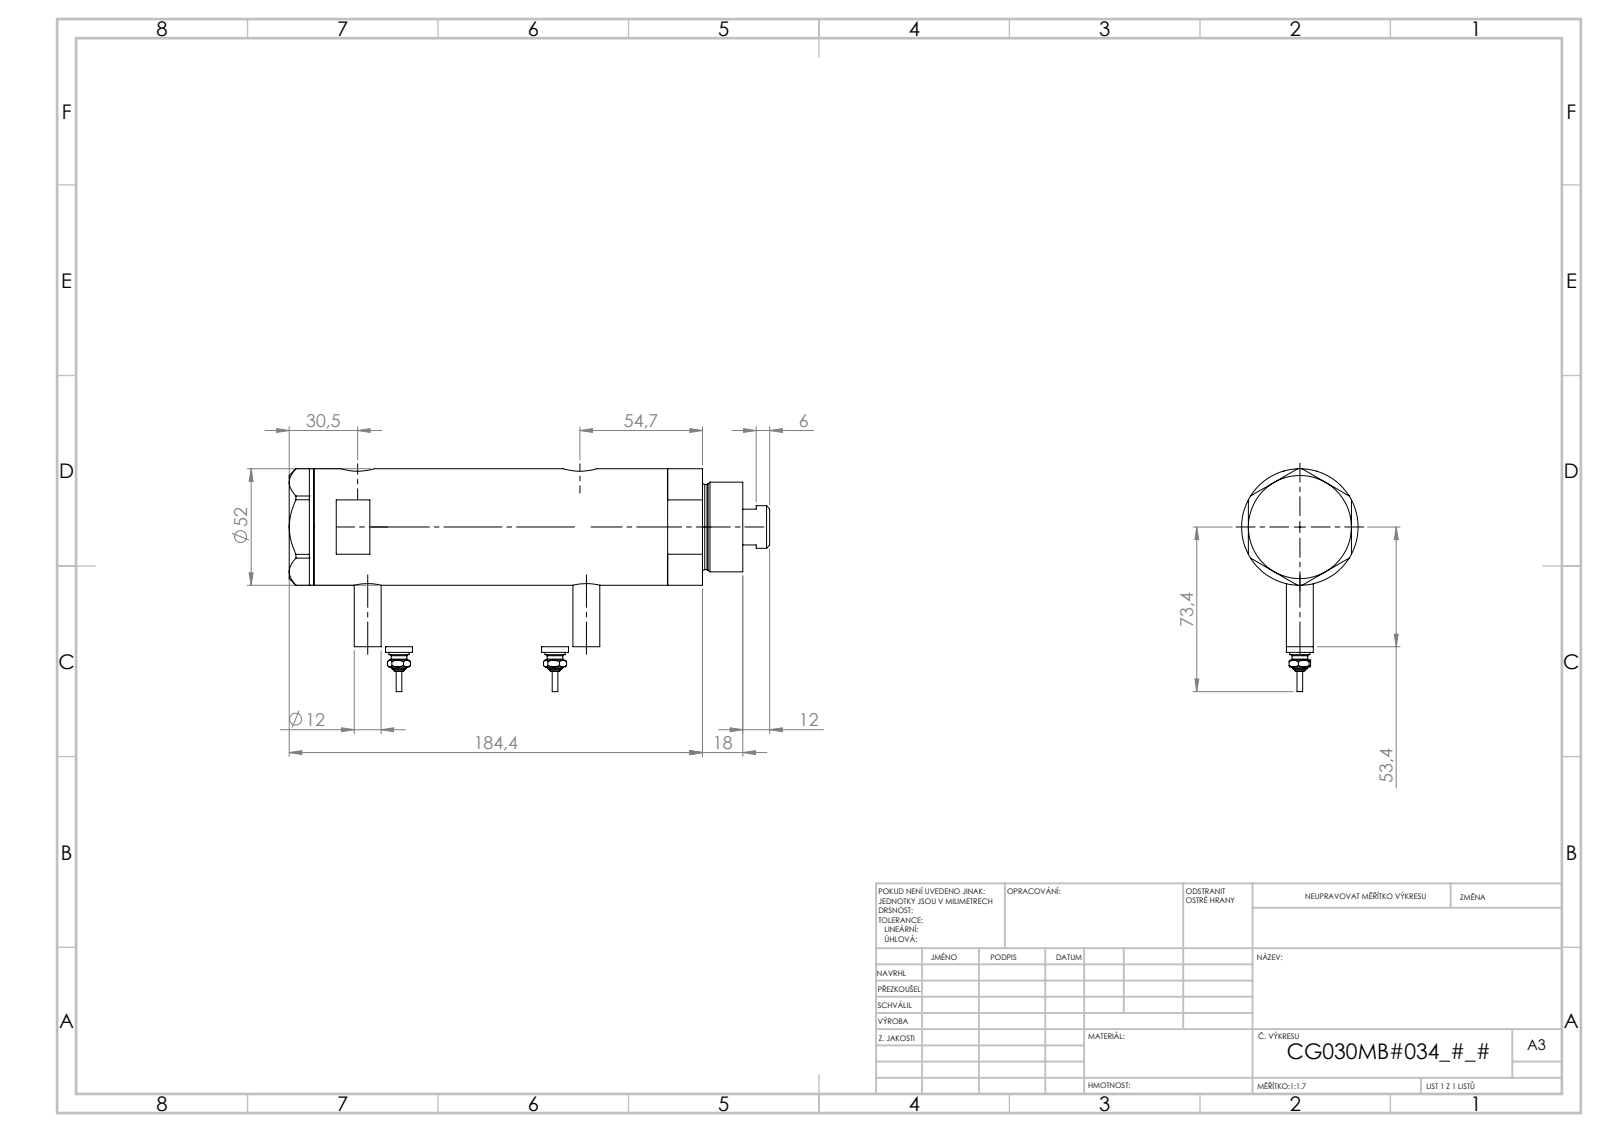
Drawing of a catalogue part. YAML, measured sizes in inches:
part_name: "V270CG_VC; V270CG_SWITCH; V270CG_BACK; V270CG_MIDDLE (+1 more)"
step_written_by: "SolidWorks 2019 (CONFIG_CONTROL_DESIGN)"
units: inches
bodies: {solids: 6, faces: 246, planar: 95, cylindrical: 77, other: 74}
overall_size: [7.206, 3.319, 2.047]
volume: 20.09
surface_area: 120.8
round_holes:
  - {diameter: 0.197, count: 2}
  - {diameter: 0.383, count: 2}
  - {diameter: 0.492, count: 2}
  - {diameter: 0.591, count: 2}
  - {diameter: 0.256, count: 1}
  - {diameter: 0.787, count: 1}
  - {diameter: 0.846, count: 1}
  - {diameter: 1.181, count: 1}
  - {diameter: 1.299, count: 1}
  - {diameter: 1.732, count: 1}
round_bosses_or_shafts:
  - {diameter: 0.472, count: 3}
  - {diameter: 0.354, count: 2}
  - {diameter: 0.276, count: 2}
  - {diameter: 0.171, count: 2}
  - {diameter: 0.094, count: 2}
  - {diameter: 2.047, count: 1}
  - {diameter: 1.575, count: 1}
  - {diameter: 1.496, count: 1}
face_to_face_distances: [0.937, 0.433, 1.37, 1.811, 3.88, 3.447, 2.51, 5.313, 4.88, 3.943]
hole_center_spacings: [0.114, 0.177, 2.392, 2.506, 2.569, 2.683, 0.114, 0.115]
